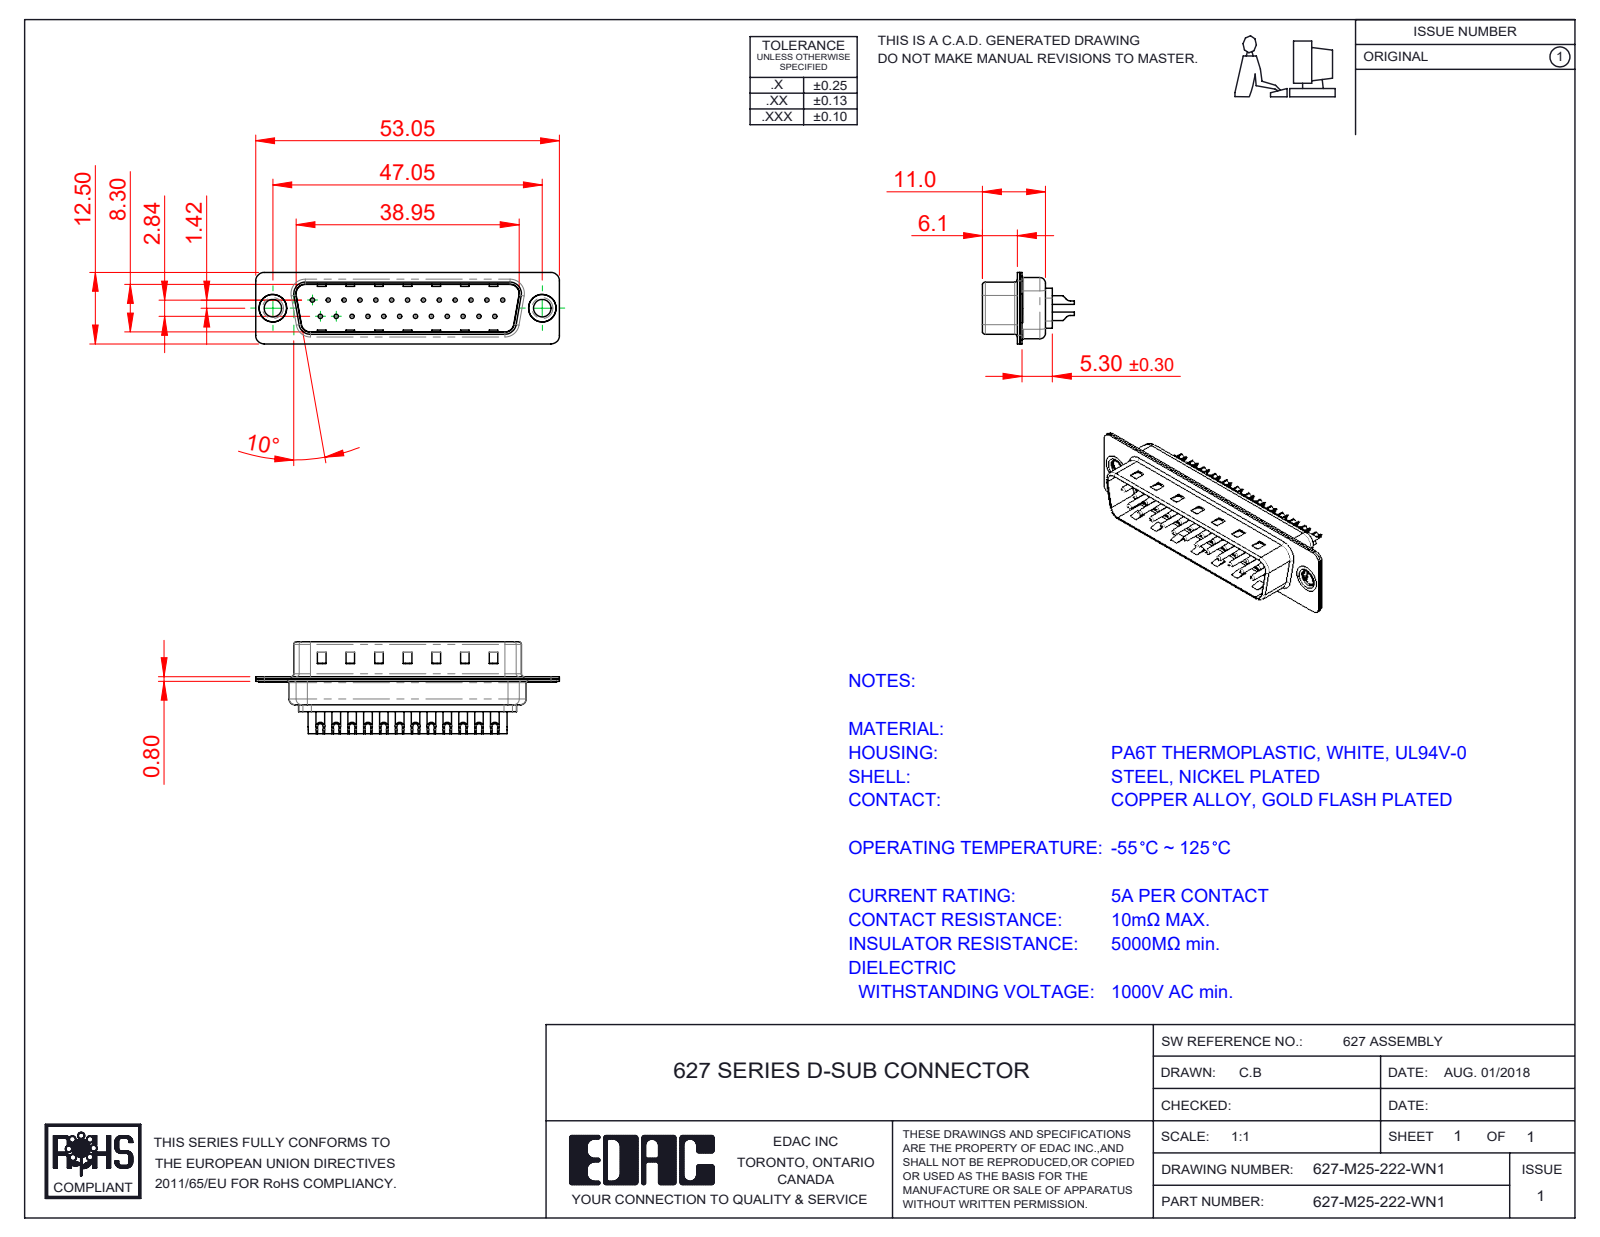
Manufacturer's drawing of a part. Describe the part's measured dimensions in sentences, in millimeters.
The part is named "627M Shell Front_25 Contacts; 627-M25-222-WN1; 627M Shell Rear_25 Contacts; 627M Contact Row 1_22 (+3 more)". Its 3-D file was written by "SolidWorks 2020 (CONFIG_CONTROL_DESIGN)". It is 30 solids with 1275 faces: 396 planar, 521 cylindrical and 358 other. Overall it measures 53.05 by 16.05 by 12.5 millimeters. Its volume is 2 698 cubic millimeters and its surface area 6 932 square millimeters. Round holes: 25 of diameter 0.75, 25 of diameter 1, 25 of diameter 1.6, 25 of diameter 2, 2 of diameter 3.05, 2 of diameter 4, 2 of diameter 4.8. Round bosses or shafts: 25 of diameter 1.5, 2 of diameter 5, 2 of diameter 4.9, 2 of diameter 3.55. Partial cylindrical surfaces (rounded edges, fillets, slot ends): 16 of radius 1.5, 12 of radius 2, 8 of radius 0.5, 8 of radius 1.6, 6 of radius 1, 4 of radius 0.25, 4 of radius 0.6, 4 of radius 0.65. The main face-to-face distances are 0.4, 0.8, 9.5, 9.1, 8.7, 9.9, 1.2, 0.75, 0.35, 6.1. The hole center spacings are 3.16, 2.77, 5.54, 8.31, 11.08, 13.85, 16.62, 5.03.
